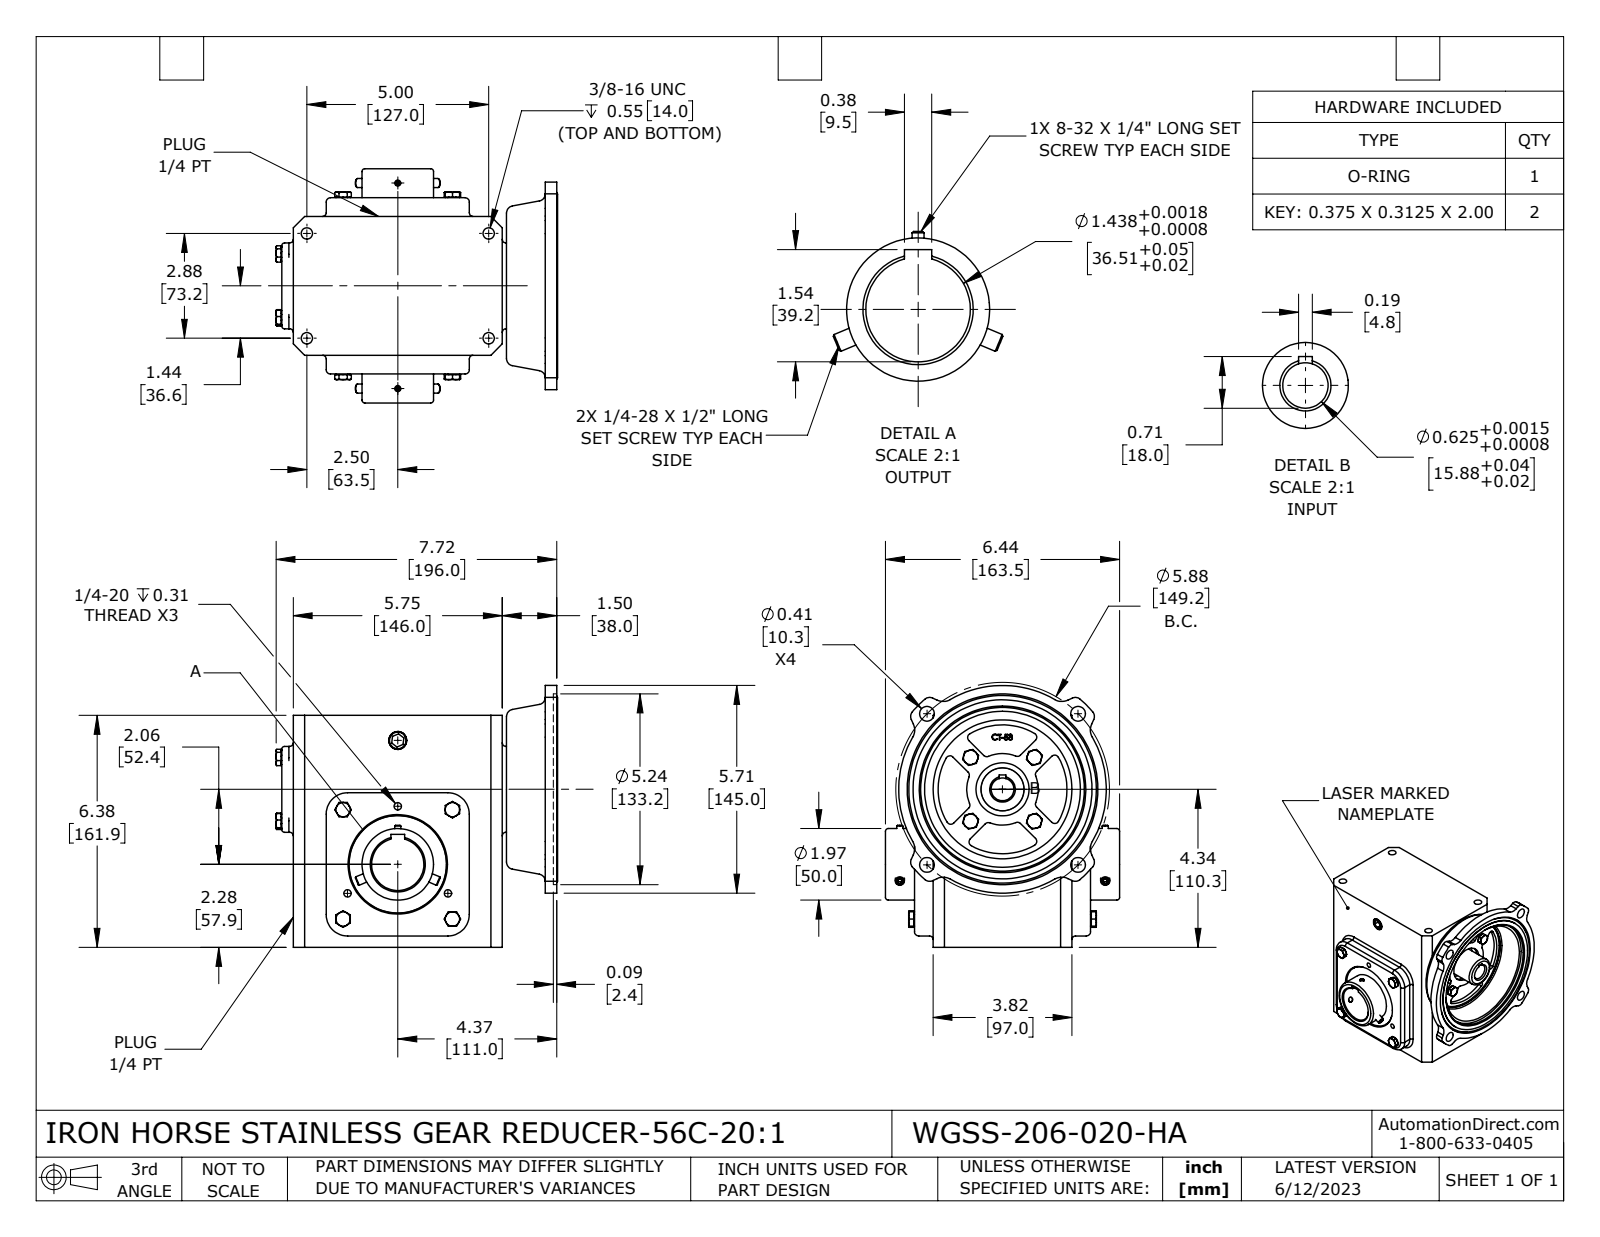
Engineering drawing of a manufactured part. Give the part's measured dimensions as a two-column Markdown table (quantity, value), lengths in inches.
| quantity | value |
| --- | --- |
| part name | WGSS-206-020-HA |
| STEP written by | SolidWorks 2021 (CONFIG_CONTROL_DESIGN) |
| units | inches |
| bodies | 7 solids, 895 faces (396 planar, 235 cylindrical, 264 other) |
| overall size | 7.74 × 7.197 × 6.437 |
| volume | 159.7 in³ |
| surface area | 323.7 in² |
| round holes (diameter × count) | 0.213 × 4, 0.313 × 4, 0.406 × 4, 0.201 × 3, 0.136 × 2, 0.625 × 1, 0.866 × 1, 1.437 × 1, 1.441 × 1, 1.457 × 1, 1.575 × 1, 3.819 × 1 |
| round bosses / shafts (diameter × count) | 0.394 × 8, 0.25 × 4, 0.164 × 2, 4.921 × 1, 2.677 × 1, 1.969 × 1, 1.181 × 1 |
| partial cylindrical surfaces (radius × count) | 0.118 × 24, 0.098 × 16, 0.394 × 12, 0.197 × 8, 0.079 × 4, 0.315 × 4, 0.591 × 4, 0.984 × 1 |
| main face-to-face distances | 6.375, 3.819, 0.512, 4.331, 5.748, 0.118, 0.315, 7.244, 4.843, 0.157 |
| hole center spacings | 2.858, 2.937, 4.154, 4.944, 1.594, 5.65, 2.762, 2.88 |
